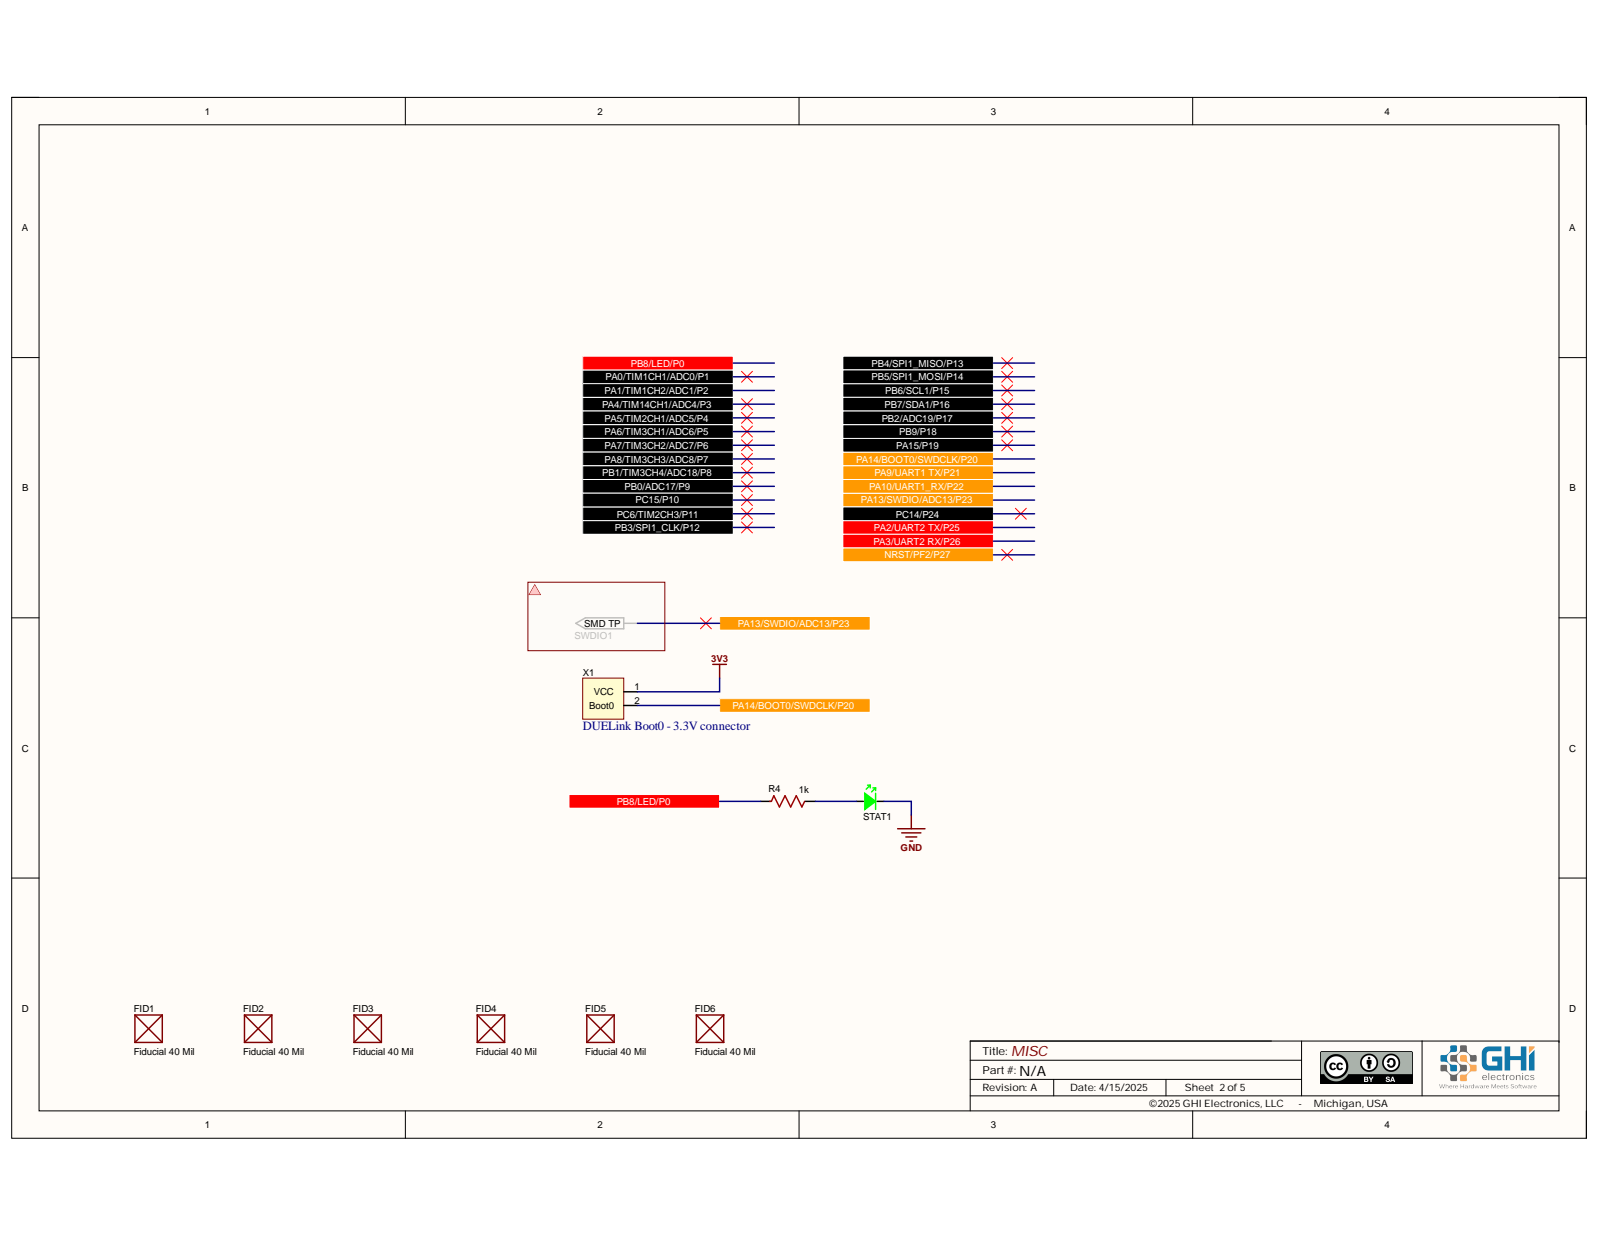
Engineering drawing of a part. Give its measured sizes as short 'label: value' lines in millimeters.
name: PCB; Board; J12; Conn_Molex_90120-0763_eec (+3 more)
written by: Open CASCADE 7.5 (AUTOMOTIVE_DESIGN)
unit: mm
bodies: 100 solids, 1911 faces (1573 planar, 236 cylindrical, 102 other)
size: 26 × 23.97 × 17
volume: 1 440 mm³; area: 2 791 mm²
holes: 7× ⌀1, 2× ⌀1.02, 2× ⌀3
bosses: 1× ⌀3
rounds: 35× R0.12, 14× R0.15, 4× R0.2, 2× R0.1, 2× R0.17, 2× R0.18, 2× R0.18, 2× R0.3
face distances: 1.6, 8.6, 7, 2.54, 10.2, 11.45, 4.3, 5, 2.4, 13.55
hole spacings: 2.54, 5.61, 10, 10.32, 4.37, 4.97, 5, 5.08
